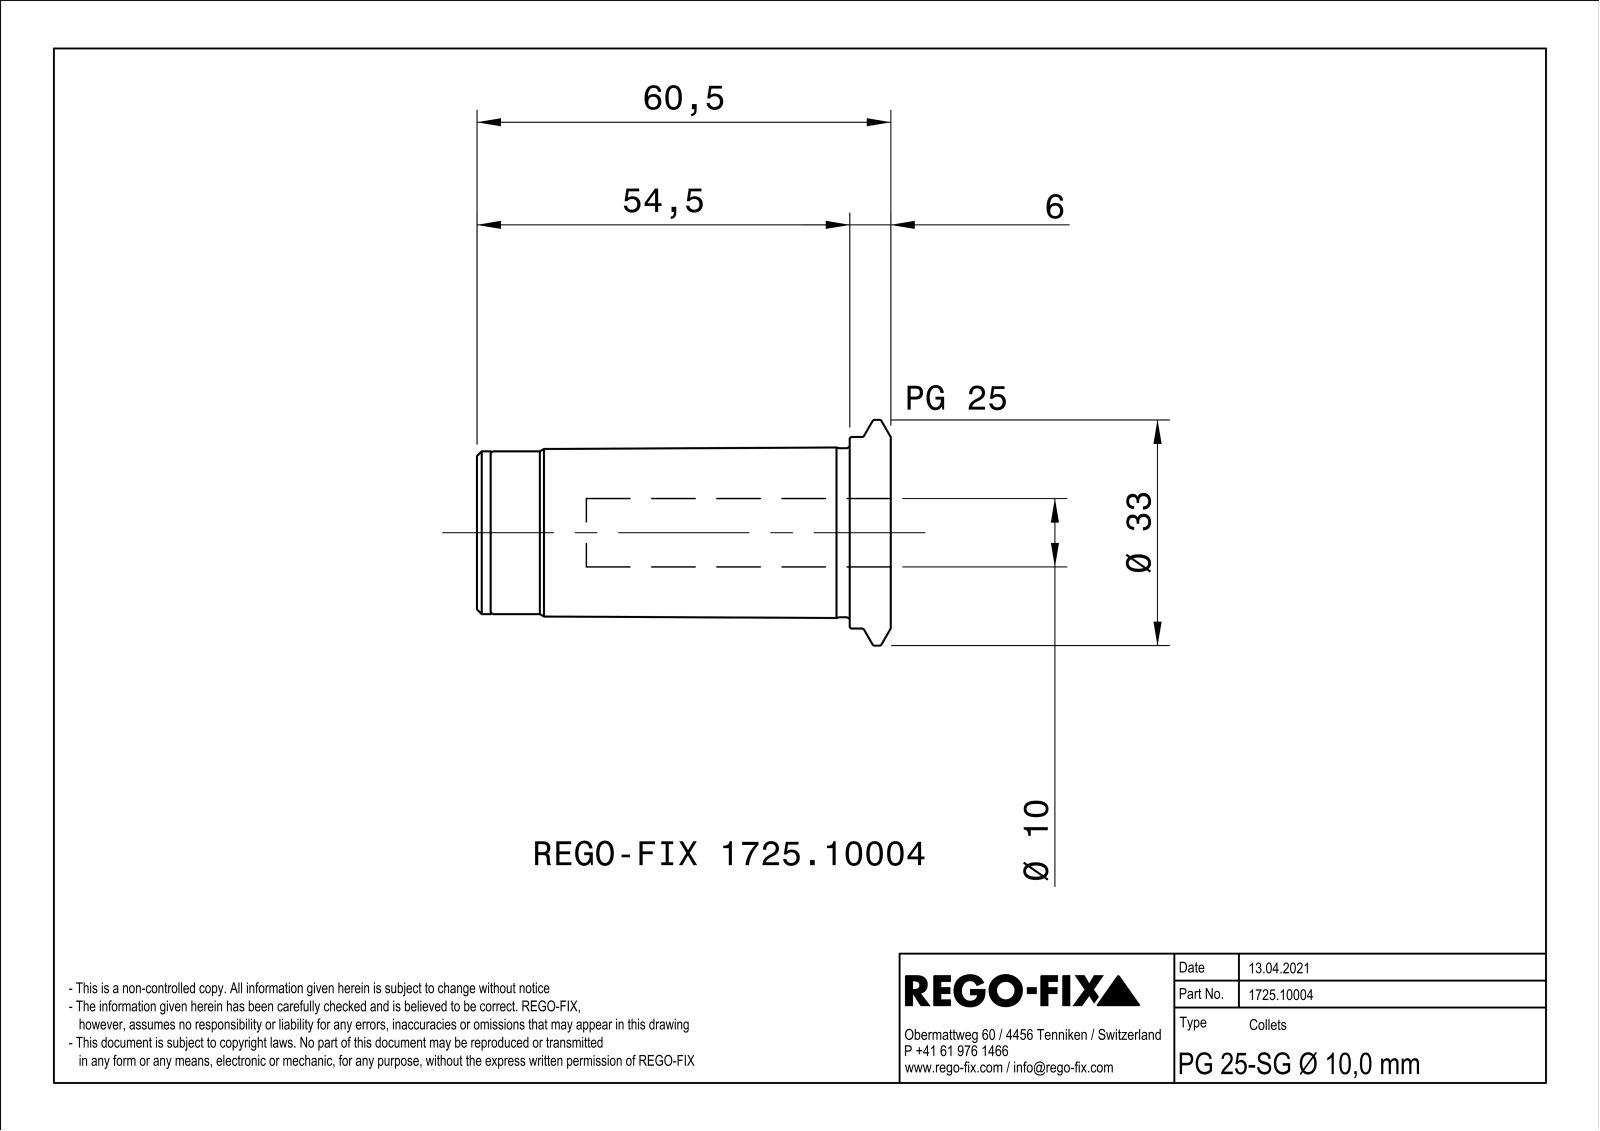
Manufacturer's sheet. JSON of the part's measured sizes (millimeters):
{"part_name": "NOCUT", "step_written_by": "SIEMENS PLM Software Solid Edge ST10 (AUTOMOTIVE_DESIGN)", "units": "millimeters", "bodies": {"solids": 1, "faces": 85, "planar": 20, "cylindrical": 26, "other": 39}, "overall_size": [60.5, 33, 32.99], "round_holes": [[2.5, 3], [5.2, 1], [6.92, 1], [8.2, 1], [10, 1], [20.4, 1], [20.92, 1], [22.2, 1]], "round_bosses_or_shafts": [[33, 1], [28, 1], [24.7, 1], [23.8, 1], [12, 1]], "partial_cylinders_radius": [[0.5, 3]], "face_to_face_distances": [1, 60.5, 52.6, 7.9, 58.5, 5.9, 2, 50, 2.6, 8.5], "hole_center_spacings": [7.75, 13.43, 13.42]}
